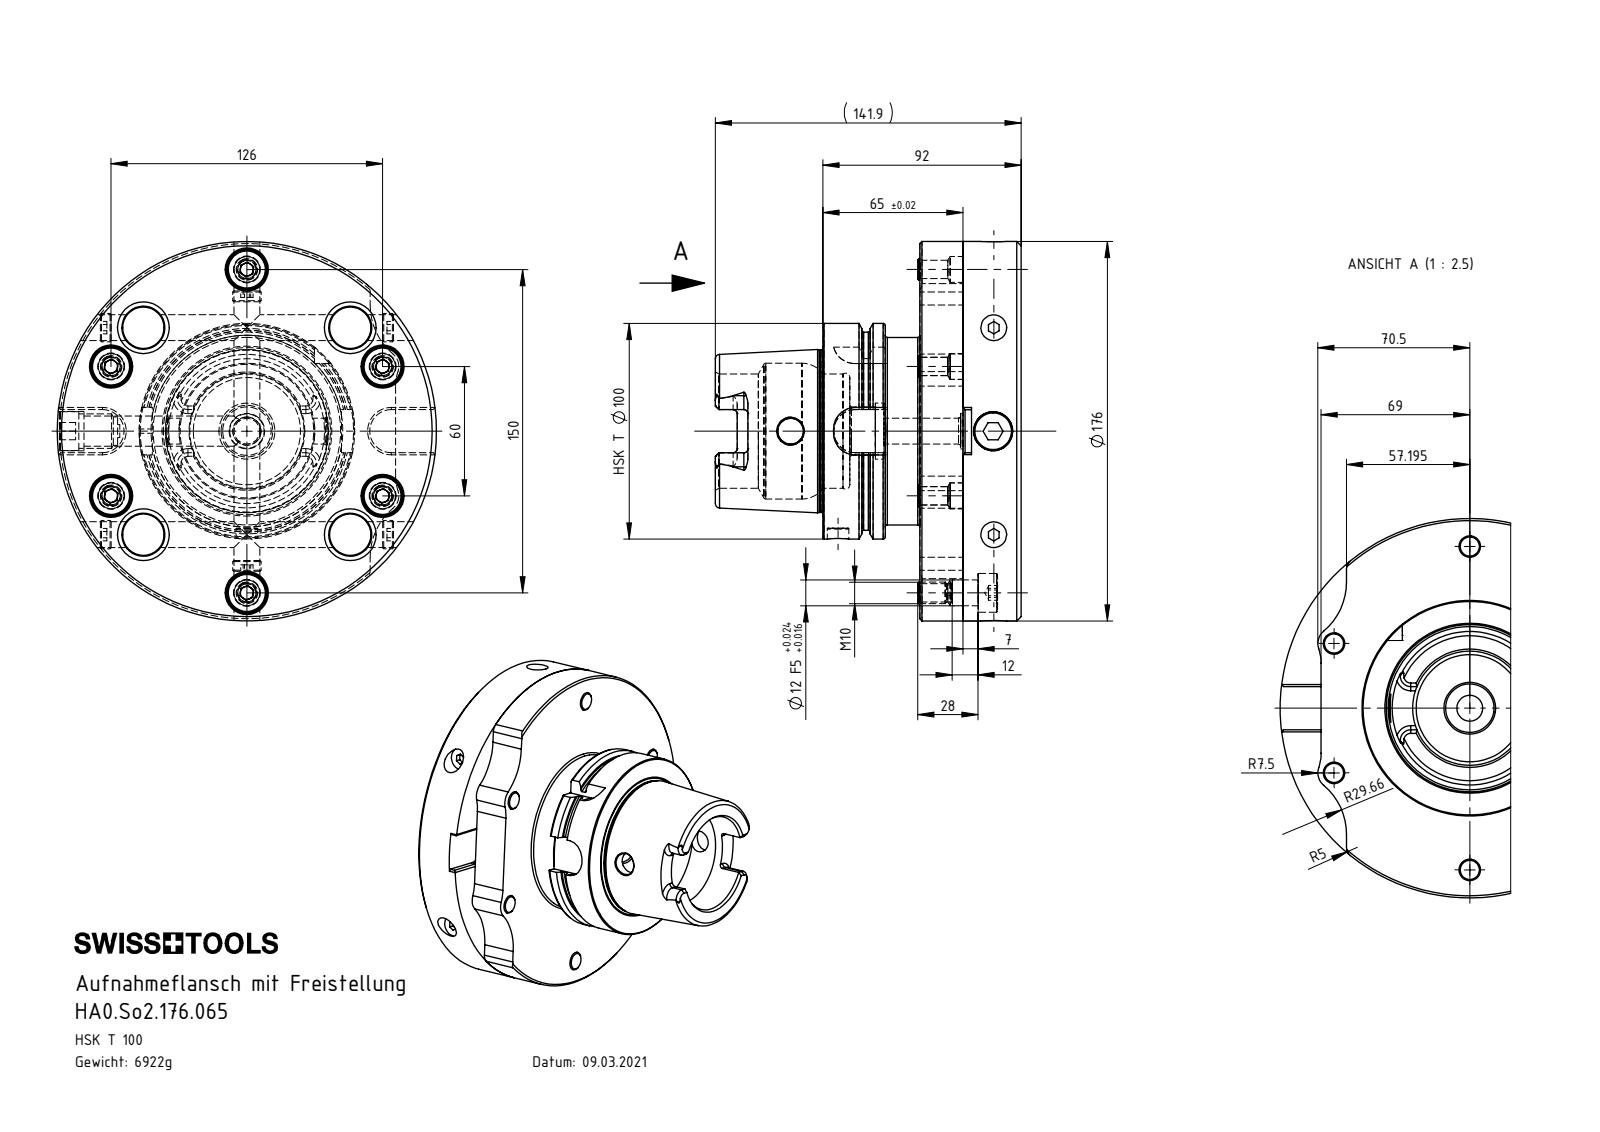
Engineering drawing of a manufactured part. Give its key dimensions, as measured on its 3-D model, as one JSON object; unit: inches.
{"part_name": "HA0-So2.176.065_A_Rohling; DIN 3771 - 13x1.5; 45800; HA0-So2.176.065 (+1 more)", "step_written_by": "SolidWorks 2017 (CONFIG_CONTROL_DESIGN)", "units": "inches", "bodies": {"solids": 16, "faces": 683, "planar": 242, "cylindrical": 236, "other": 205}, "overall_size": [6.929, 6.929, 5.587], "volume_in3": 82.44, "surface_area_in2": 324.5, "round_holes": [[0.472, 11], [0.787, 10], [0.335, 6], [0.748, 6], [0.394, 1], [0.551, 1], [0.65, 1], [0.719, 1], [0.886, 1], [1.024, 1], [2.087, 1], [2.48, 1]], "round_bosses_or_shafts": [[0.709, 7], [0.394, 6], [0.331, 6], [0.518, 3], [6.929, 1], [3.937, 1], [3.62, 1], [3.425, 1]], "partial_cylinders_radius": [[0.075, 6], [0.394, 6], [0.19, 2], [0.192, 2], [0.197, 2], [0.295, 2], [0.827, 2], [1.168, 2]], "face_to_face_distances": [1.063, 0.787, 1.85, 1.772, 2.559, 3.622, 0.157, 0.945, 2.717, 0.906], "hole_center_spacings": [3.78, 0.922, 2.168, 2.672, 2.747, 3.048, 3.127, 4.427]}
